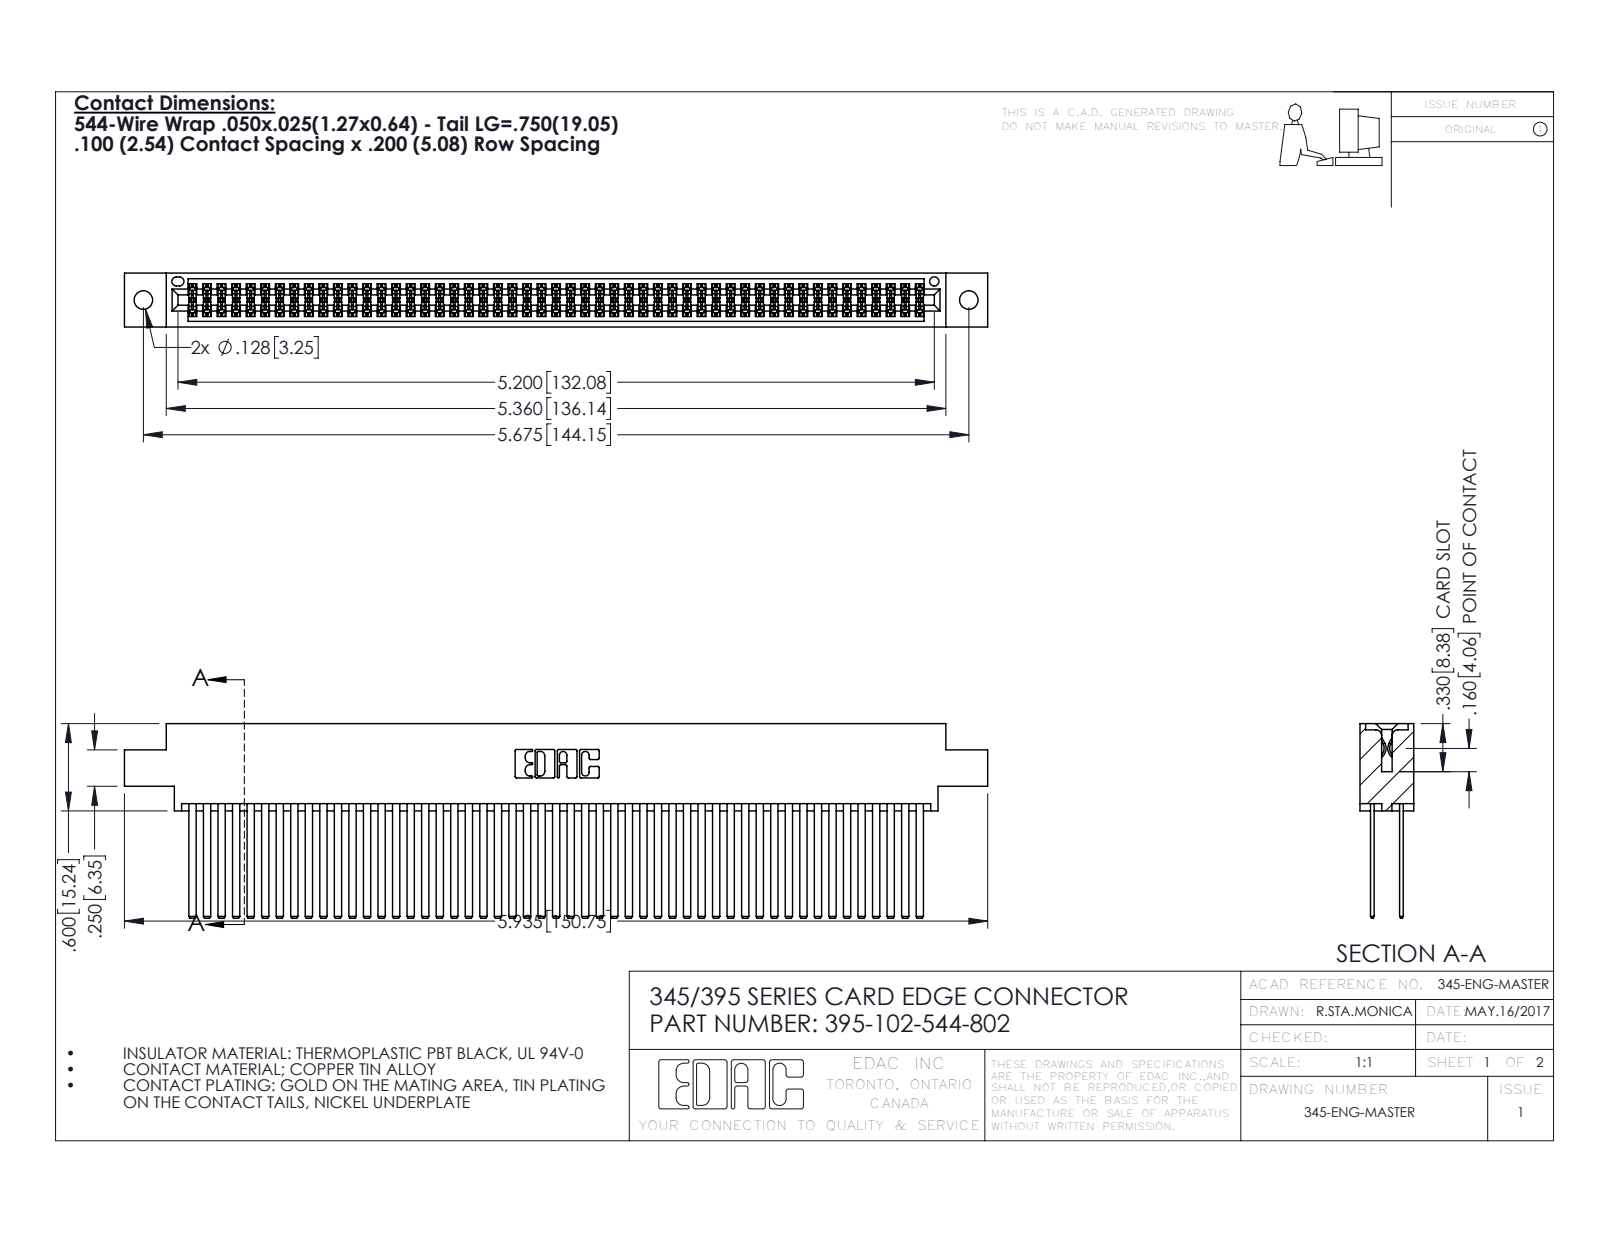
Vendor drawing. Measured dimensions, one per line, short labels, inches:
name: 395-102-544-802; 345-292-001_345-293-144; 345 Part_0.170 Offset - 0.128 Dia
written by: SolidWorks 2016 (CONFIG_CONTROL_DESIGN)
unit: in
bodies: 103 solids, 4618 faces (3042 planar, 1576 cylindrical, 0 other)
size: 5.935 × 1.337 × 0.37
volume: 0.977 in³; area: 43.24 in²
holes: 2× ⌀0.128, 1× ⌀0.064
rounds: 153× R0.006, 22× R0.01, 6× R0.007, 6× R0.031, 3× R0.026, 2× R0.014, 2× R0.019, 2× R0.022
face distances: 0.2, 0.025, 0.298, 0.072, 0.098, 0.272, 0.225, 0.175, 0.37, 0.15
hole spacings: 0.27, 5.439, 5.675
